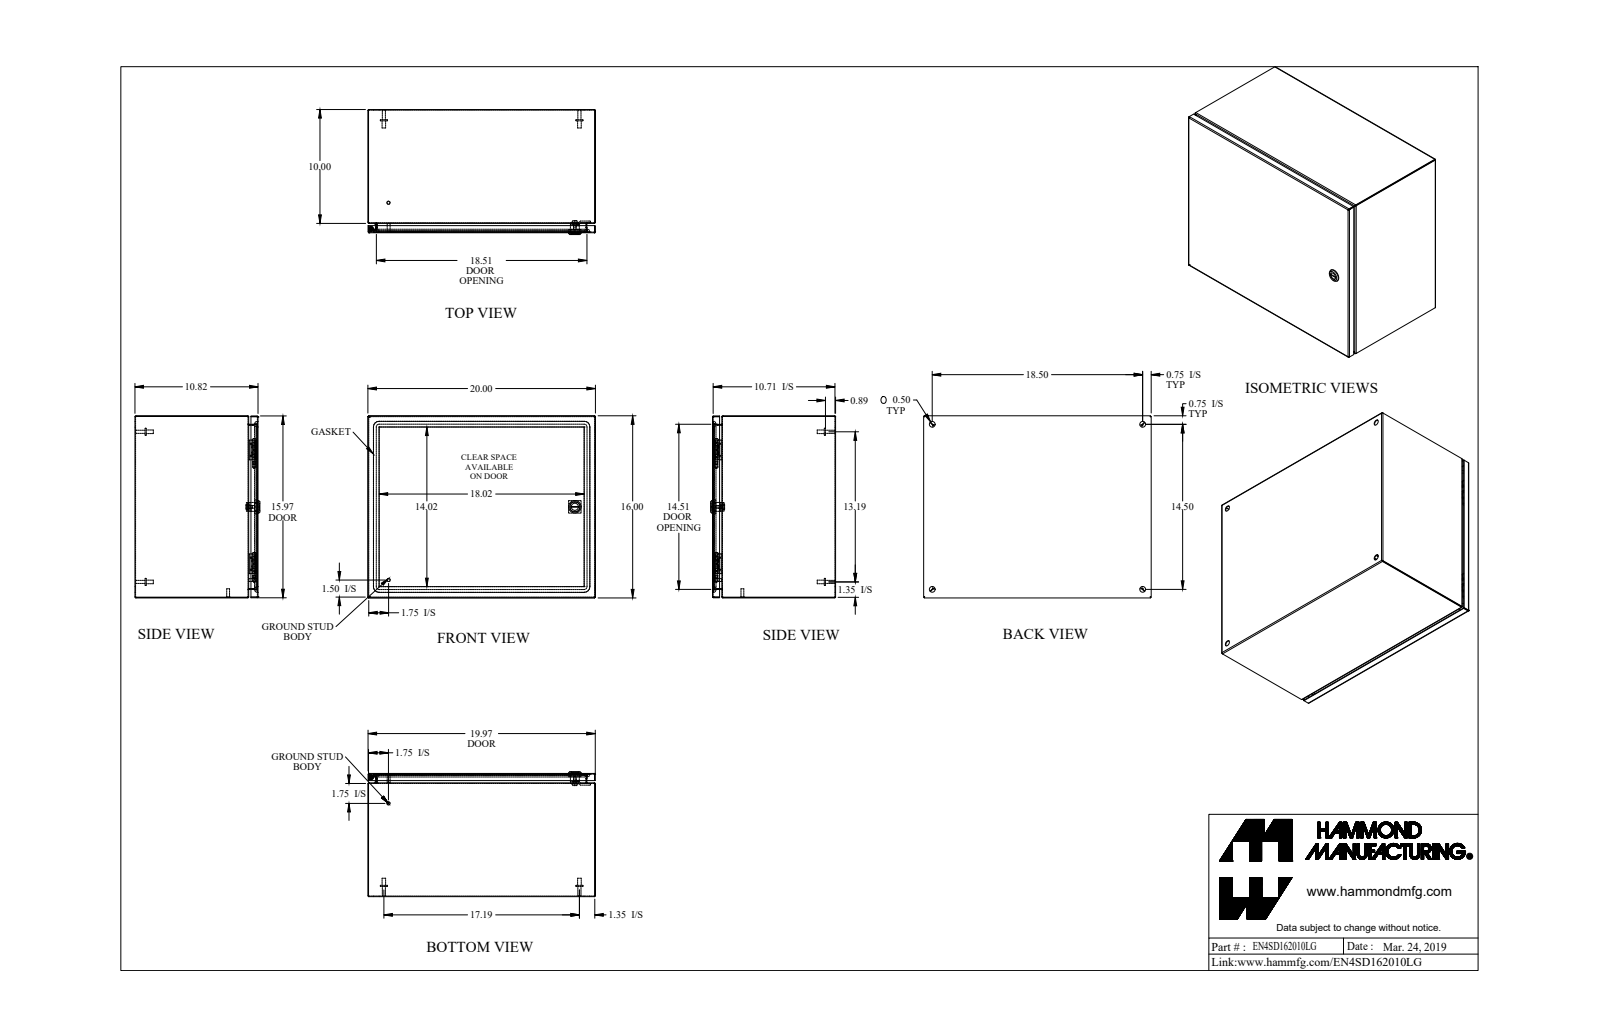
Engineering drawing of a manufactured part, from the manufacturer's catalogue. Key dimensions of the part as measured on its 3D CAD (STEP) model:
Part name (STEP PRODUCT): EN4SD162010LG_Default
STEP written by: SolidWorks 2019 (CONFIG_CONTROL_DESIGN)
Units: inches
Bodies: 21 solids, 634 faces (285 planar, 213 cylindrical, 136 other)
Overall size (bounding box): 20 × 16 × 10.982
Volume: 92.6 in³ · Surface area: 3 159 in²
Round holes (diameter × count): ⌀0.5 ×4, ⌀0.172 ×1, ⌀0.232 ×1, ⌀0.24 ×1, ⌀0.242 ×1, ⌀0.625 ×1, ⌀0.785 ×1
Round bosses / shafts (diameter × count): ⌀0.625 ×4, ⌀0.313 ×4, ⌀0.27 ×4, ⌀0.281 ×2, ⌀0.25 ×2, ⌀1.1 ×1, ⌀0.525 ×1, ⌀0.455 ×1
Partial cylindrical surfaces — rounded edges, fillets, slot ends (radius × count): R0.029 ×21, R0.086 ×21, R0.25 ×16, R19 ×8, R0.006 ×4, R0.062 ×4, R0.499 ×4, R0.125 ×2
Main face-to-face distances: 0.057, 10.765, 15.943, 10.708, 10.822, 19.943, 15.886, 16, 19.886, 20
Hole centre spacings: 14.5, 18.5, 18.888, 23.506, 7.326, 7.327
